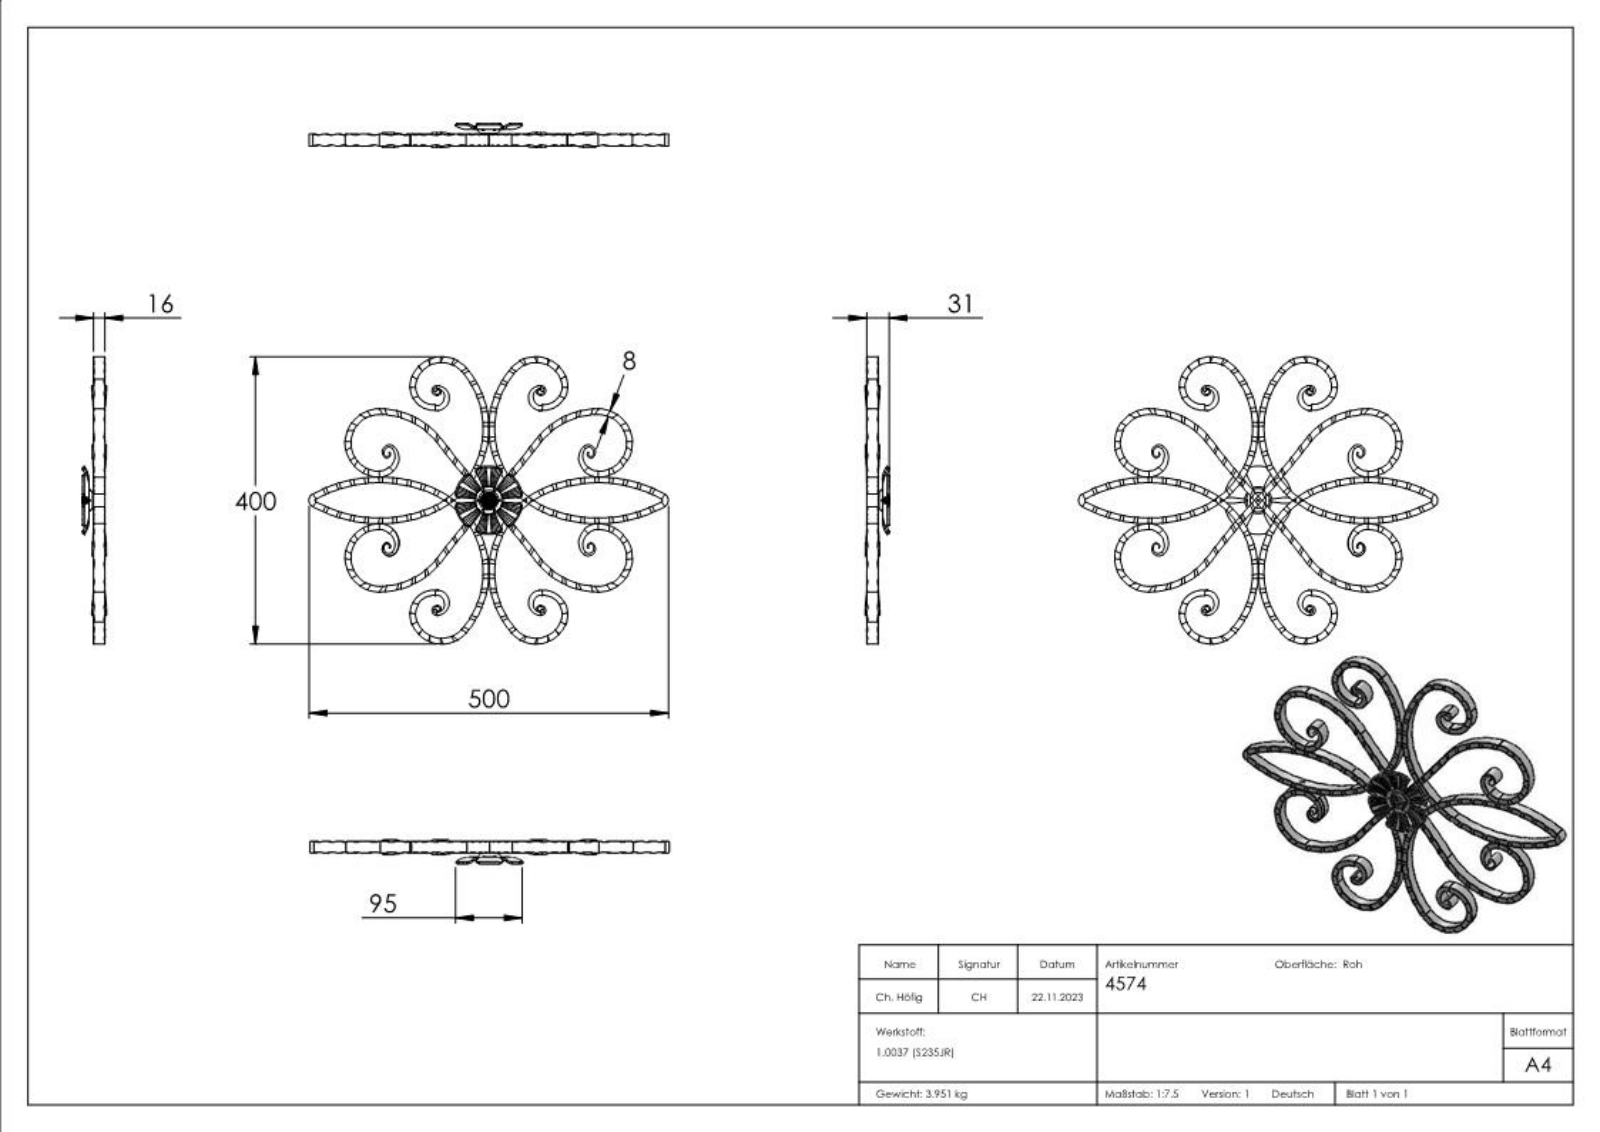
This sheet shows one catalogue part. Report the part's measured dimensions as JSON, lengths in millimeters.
{"part_name": "4574", "step_written_by": "SolidWorks 2018 (CONFIG_CONTROL_DESIGN)", "units": "millimeters", "bodies": {"solids": 7, "faces": 1658, "planar": 824, "cylindrical": 506, "other": 328}, "overall_size": [500, 400, 33.23], "volume_mm3": 506483, "surface_area_mm2": 212775, "round_bosses_or_shafts": [[22, 1], [10, 1]], "partial_cylinders_radius": [[28.62, 344], [110, 16], [1, 6], [19.49, 4], [25.55, 4], [27.49, 4], [33.55, 4], [37, 4]], "face_to_face_distances": [16, 2, 18, 20, 27.08, 25.08, 9.08, 7.08, 10, 8]}
